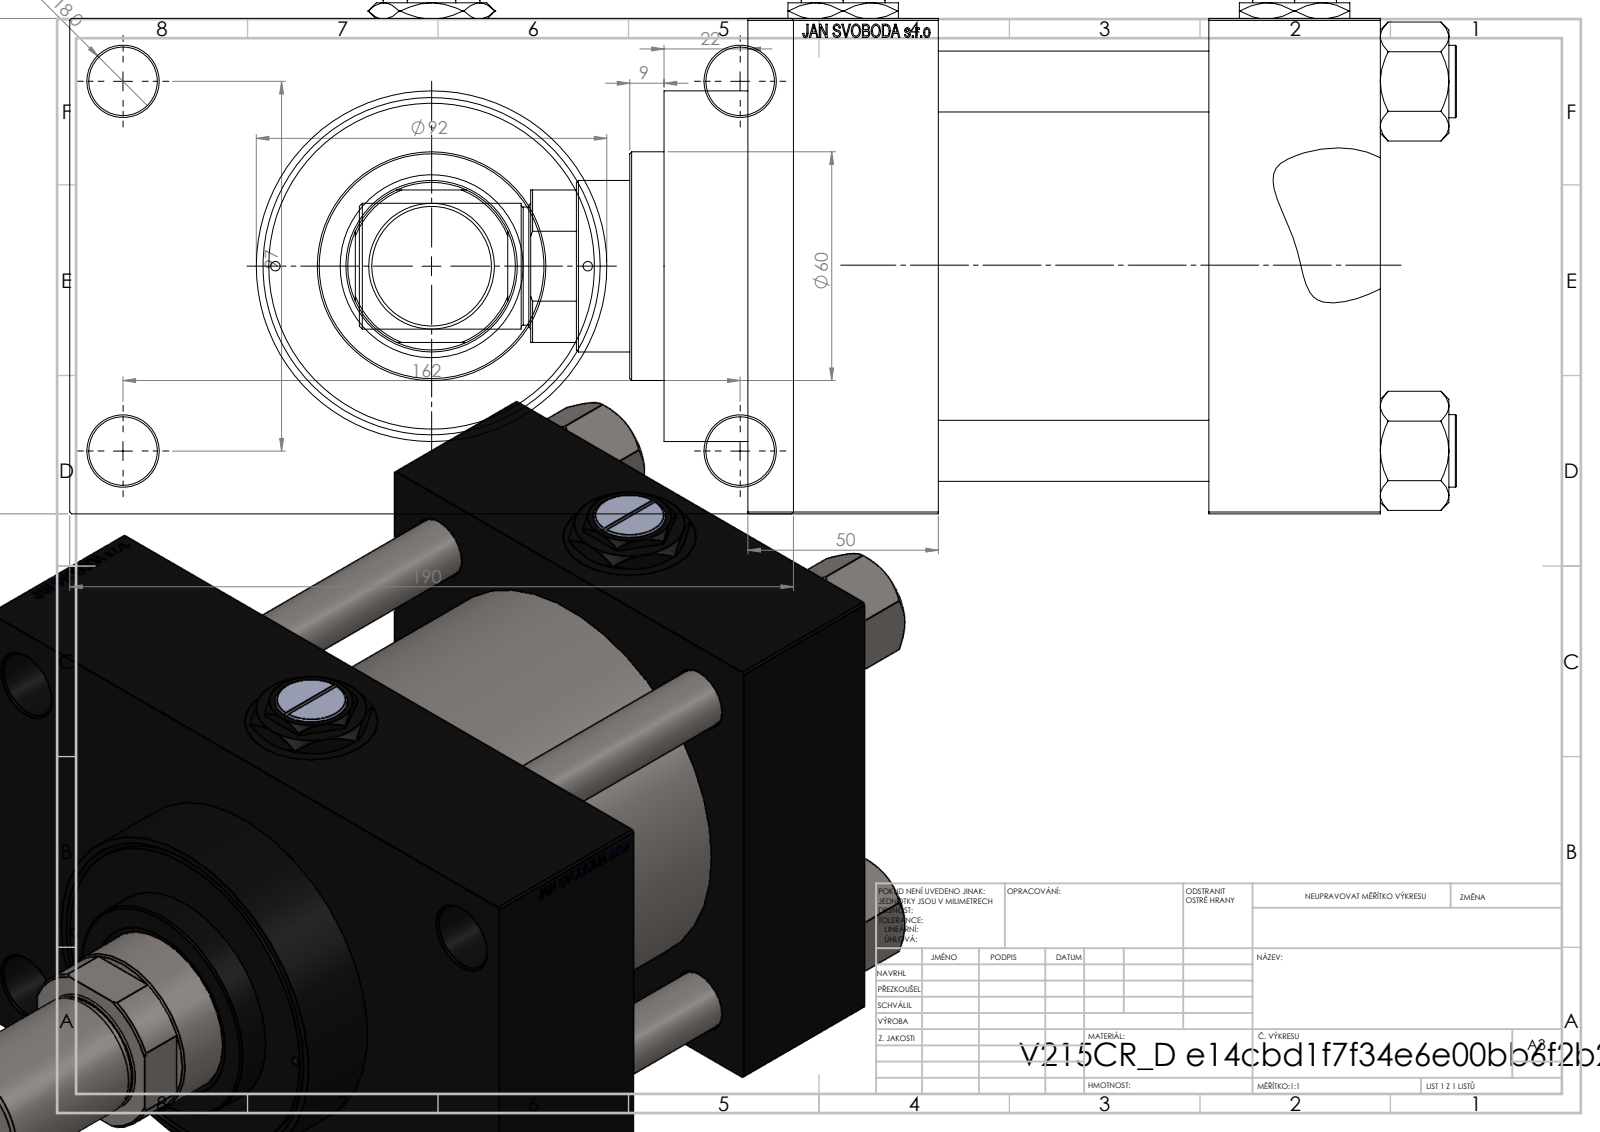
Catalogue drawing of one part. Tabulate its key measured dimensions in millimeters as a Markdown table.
| quantity | value |
| --- | --- |
| part name | V215_VC_A; V215CR_D_TYCINKA; V215CR_VCP_D; NUT_M5_D (+3 more) |
| STEP written by | SolidWorks 2019 (CONFIG_CONTROL_DESIGN) |
| units | millimeters |
| bodies | 14 solids, 1274 faces (599 planar, 107 cylindrical, 568 other) |
| overall size | 288 × 190 × 137 |
| volume | 2 614 000 mm³ |
| surface area | 368 104 mm² |
| round holes (diameter × count) | 16 × 4, 18 × 4, 26.44 × 4, 35 × 4, 7 × 3, 2.5 × 2, 31.5 × 1, 45 × 1, 48 × 1, 76 × 1, 85.5 × 1, 100 × 1 |
| round bosses / shafts (diameter × count) | 19 × 4, 106 × 1, 92 × 1, 60 × 1, 33 × 1, 31 × 1 |
| partial cylindrical surfaces (radius × count) | 22 × 1 |
| main face-to-face distances | 45, 130, 116, 71, 166, 121, 50, 30, 160, 20 |
| hole center spacings | 32.55, 49.02, 62.87, 68.52, 94.41, 96.9, 101.73, 102.27 |
